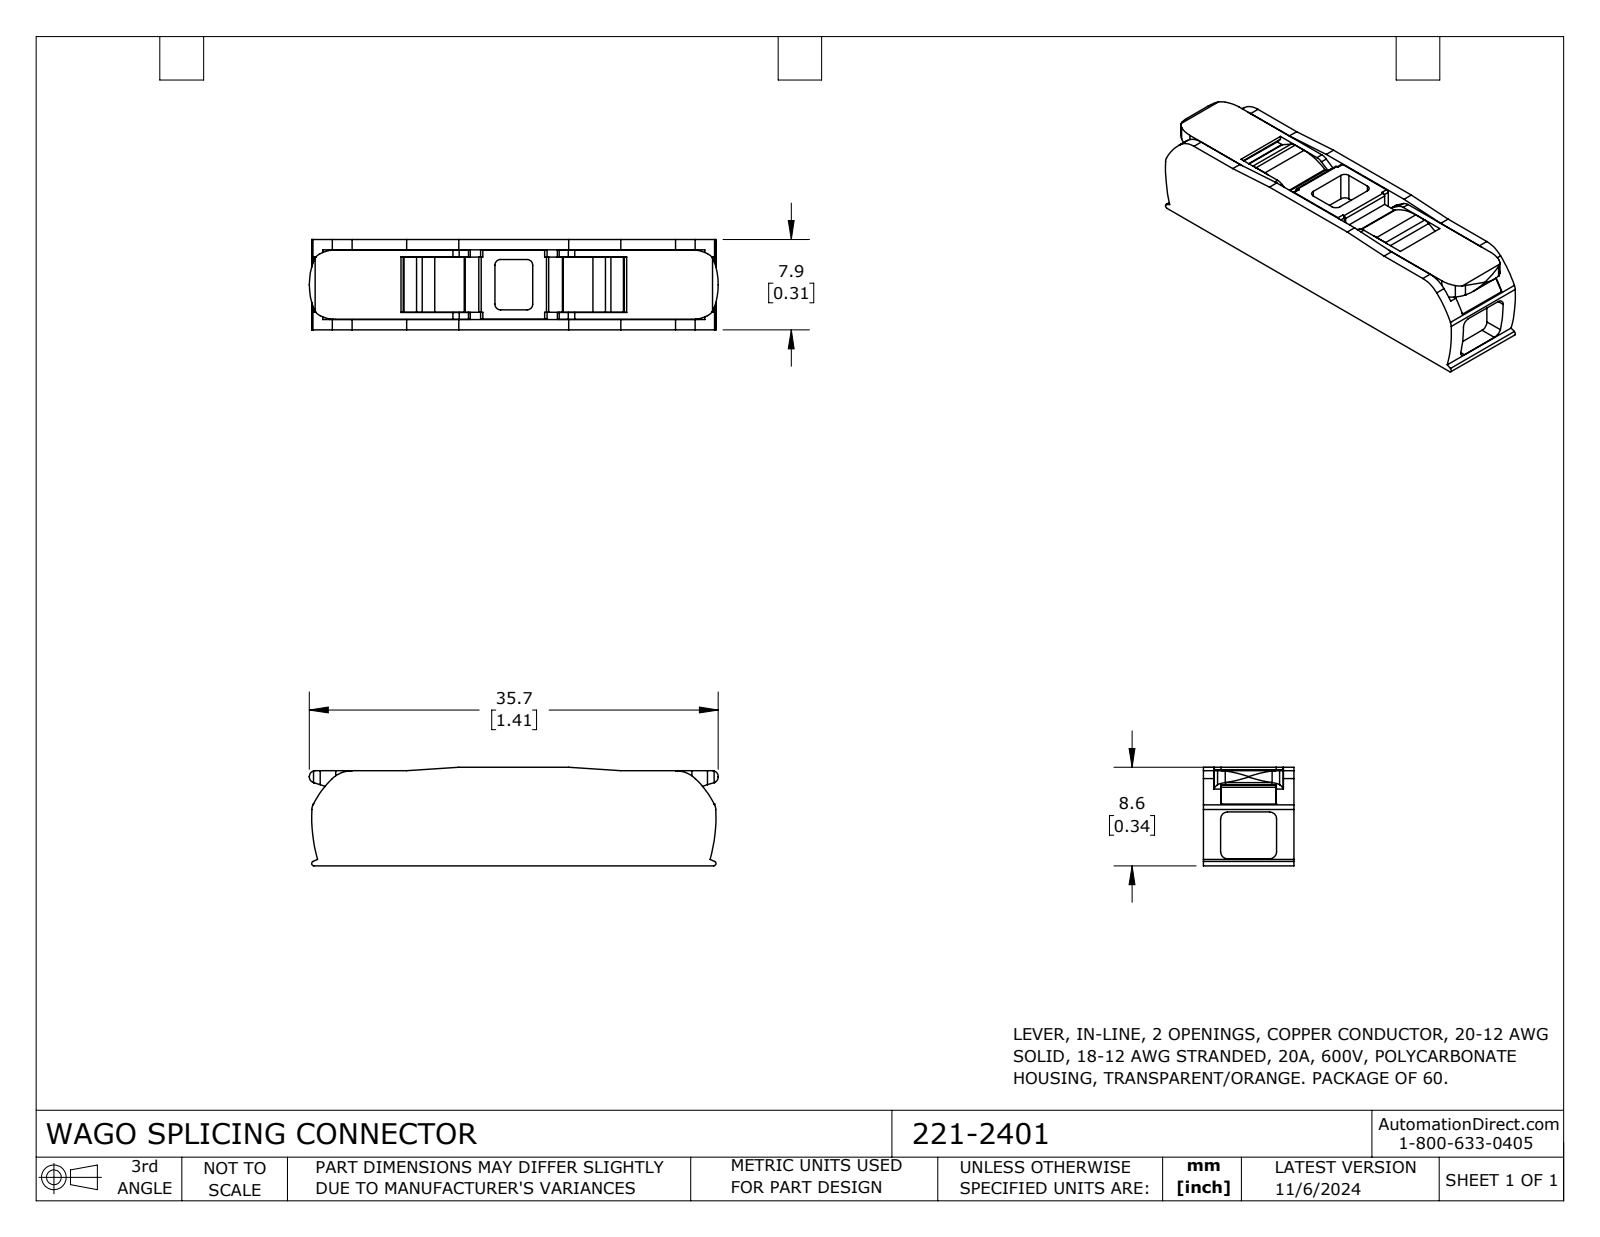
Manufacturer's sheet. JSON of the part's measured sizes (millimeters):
{"part_name": "221-2401", "step_written_by": "SolidWorks 2023 (CONFIG_CONTROL_DESIGN)", "units": "millimeters", "bodies": {"solids": 1, "faces": 177, "planar": 105, "cylindrical": 72, "other": 0}, "overall_size": [35.7, 8.6, 7.9], "volume_mm3": 2121, "surface_area_mm2": 2174, "partial_cylinders_radius": [[0.5, 10], [0.2, 6], [1, 6], [0.15, 4], [0.6, 4], [1.2, 4], [3, 4], [0.35, 2]], "face_to_face_distances": [7.9, 5.46, 0.62, 7, 0.9, 1.54, 6.36, 0.64, 5.44, 6.08]}
